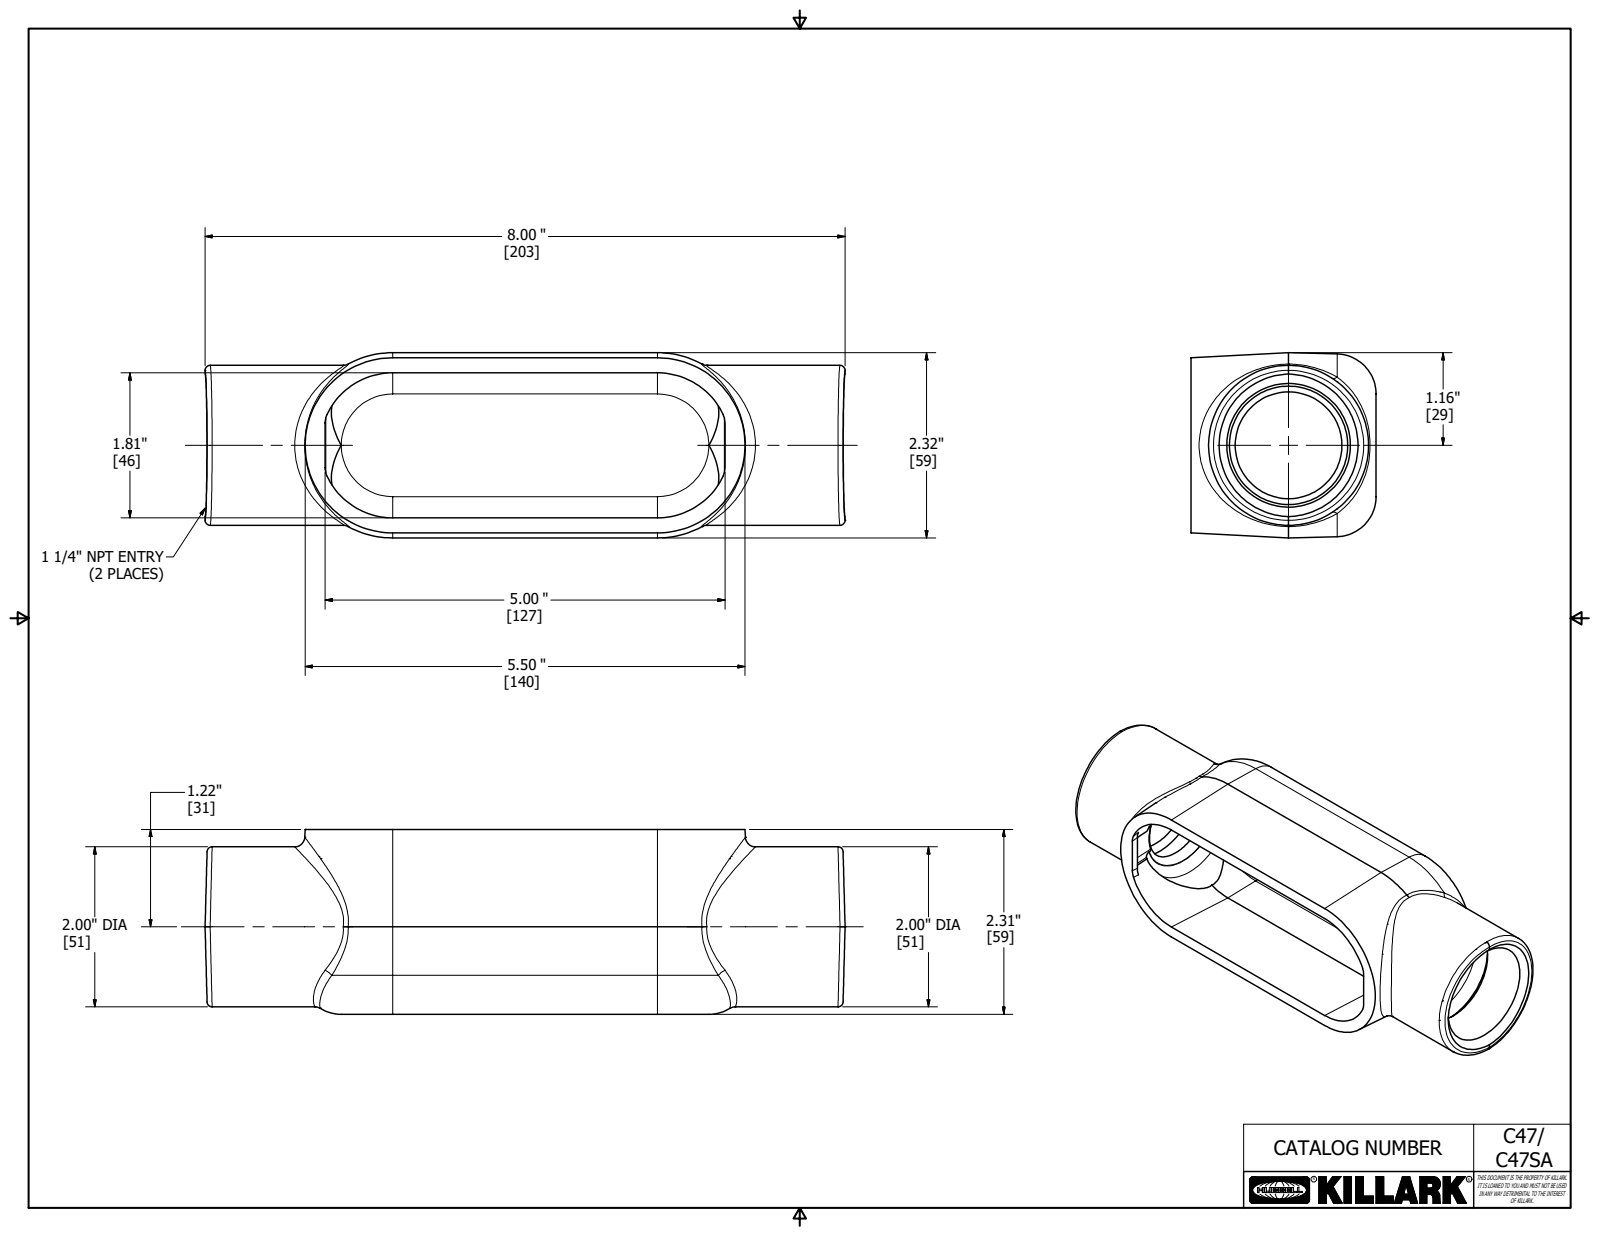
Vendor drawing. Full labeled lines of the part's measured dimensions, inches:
Part name (STEP PRODUCT): 17681
STEP written by: Autodesk Inventor 2018 (AUTOMOTIVE_DESIGN)
Units: inches
Bodies: 1 solid, 100 faces (34 planar, 18 cylindrical, 48 other)
Overall size (bounding box): 8.003 × 2.316 × 2.312
Volume: 9.429 in³ · Surface area: 103.7 in²
Round holes (diameter × count): ⌀1.666 ×1, ⌀1.813 ×1
Round bosses / shafts (diameter × count): ⌀2 ×1
Partial cylindrical surfaces — rounded edges, fillets, slot ends (radius × count): R0.05 ×4, R0.125 ×4, R0.313 ×2, R0.5 ×2
Main face-to-face distances: 0.187, 0.188, 2.312, 2.125, 0.031, 0.156, 2.281, 8.002, 2.203, 2.172
